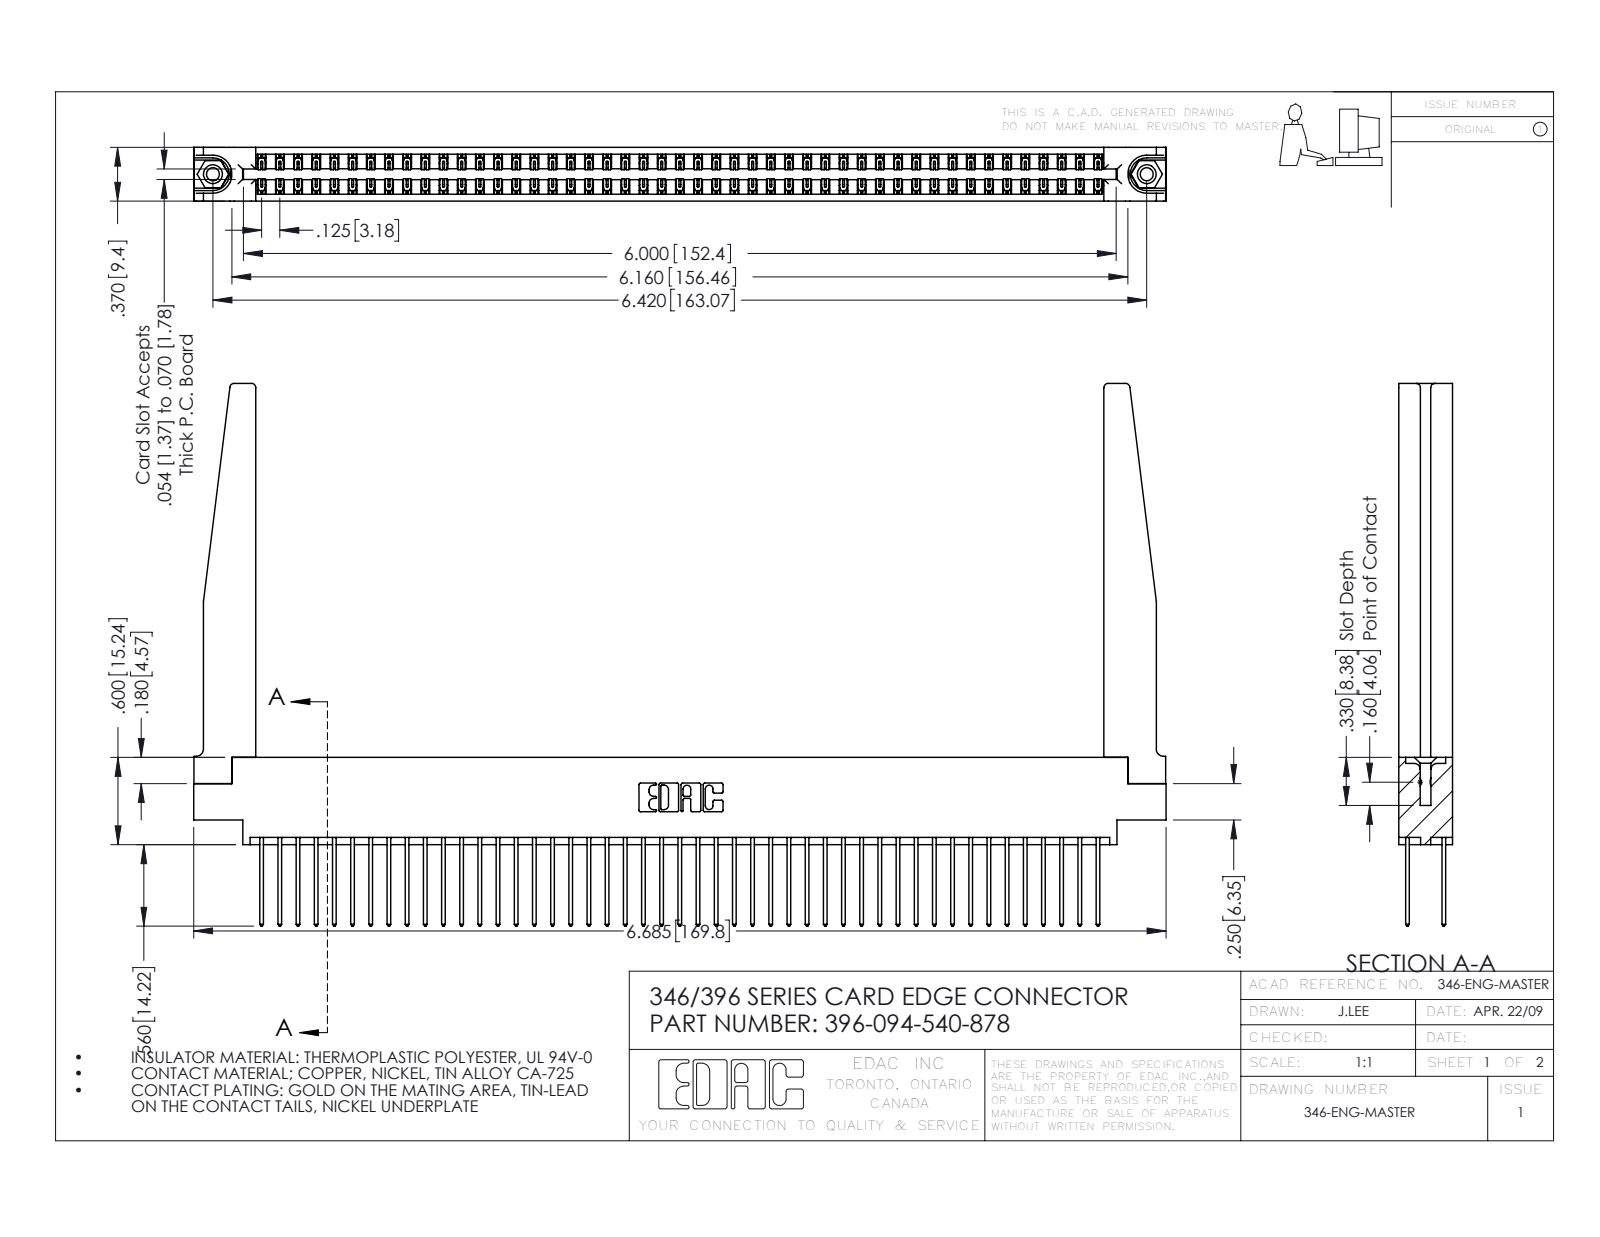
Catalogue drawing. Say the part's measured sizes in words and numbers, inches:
The part is named "346-220-078_345-220-078; 345-292-001_345-293-140; 396-094-540-878; 345-250-001_345-250-001-102 (+1 more)". Its 3-D file was written by "SolidWorks 2016 (CONFIG_CONTROL_DESIGN)". It is 99 solids with 5248 faces: 3512 planar, 1684 cylindrical and 52 other. Overall it measures 6.685 by 3.73 by 0.37 inches. Its volume is 1.447 cubic inches and its surface area 48.94 square inches. Round holes: 2 of diameter 0.089, 2 of diameter 0.125, 2 of diameter 0.156, 1 of diameter 0.064. Round bosses or shafts: 2 of diameter 0.155. Partial cylindrical surfaces (rounded edges, fillets, slot ends): 141 of radius 0.006, 94 of radius 0.01, 22 of radius 0.01, 8 of radius 0.03, 6 of radius 0.007, 6 of radius 0.031, 3 of radius 0.026, 2 of radius 0.014. The main face-to-face distances are 0.048, 0.322, 0.37, 0.072, 0.25, 0.298, 0.025, 0.275, 0.15, 0.148. The hole center spacings are 0.246, 6.211, 6.42.
